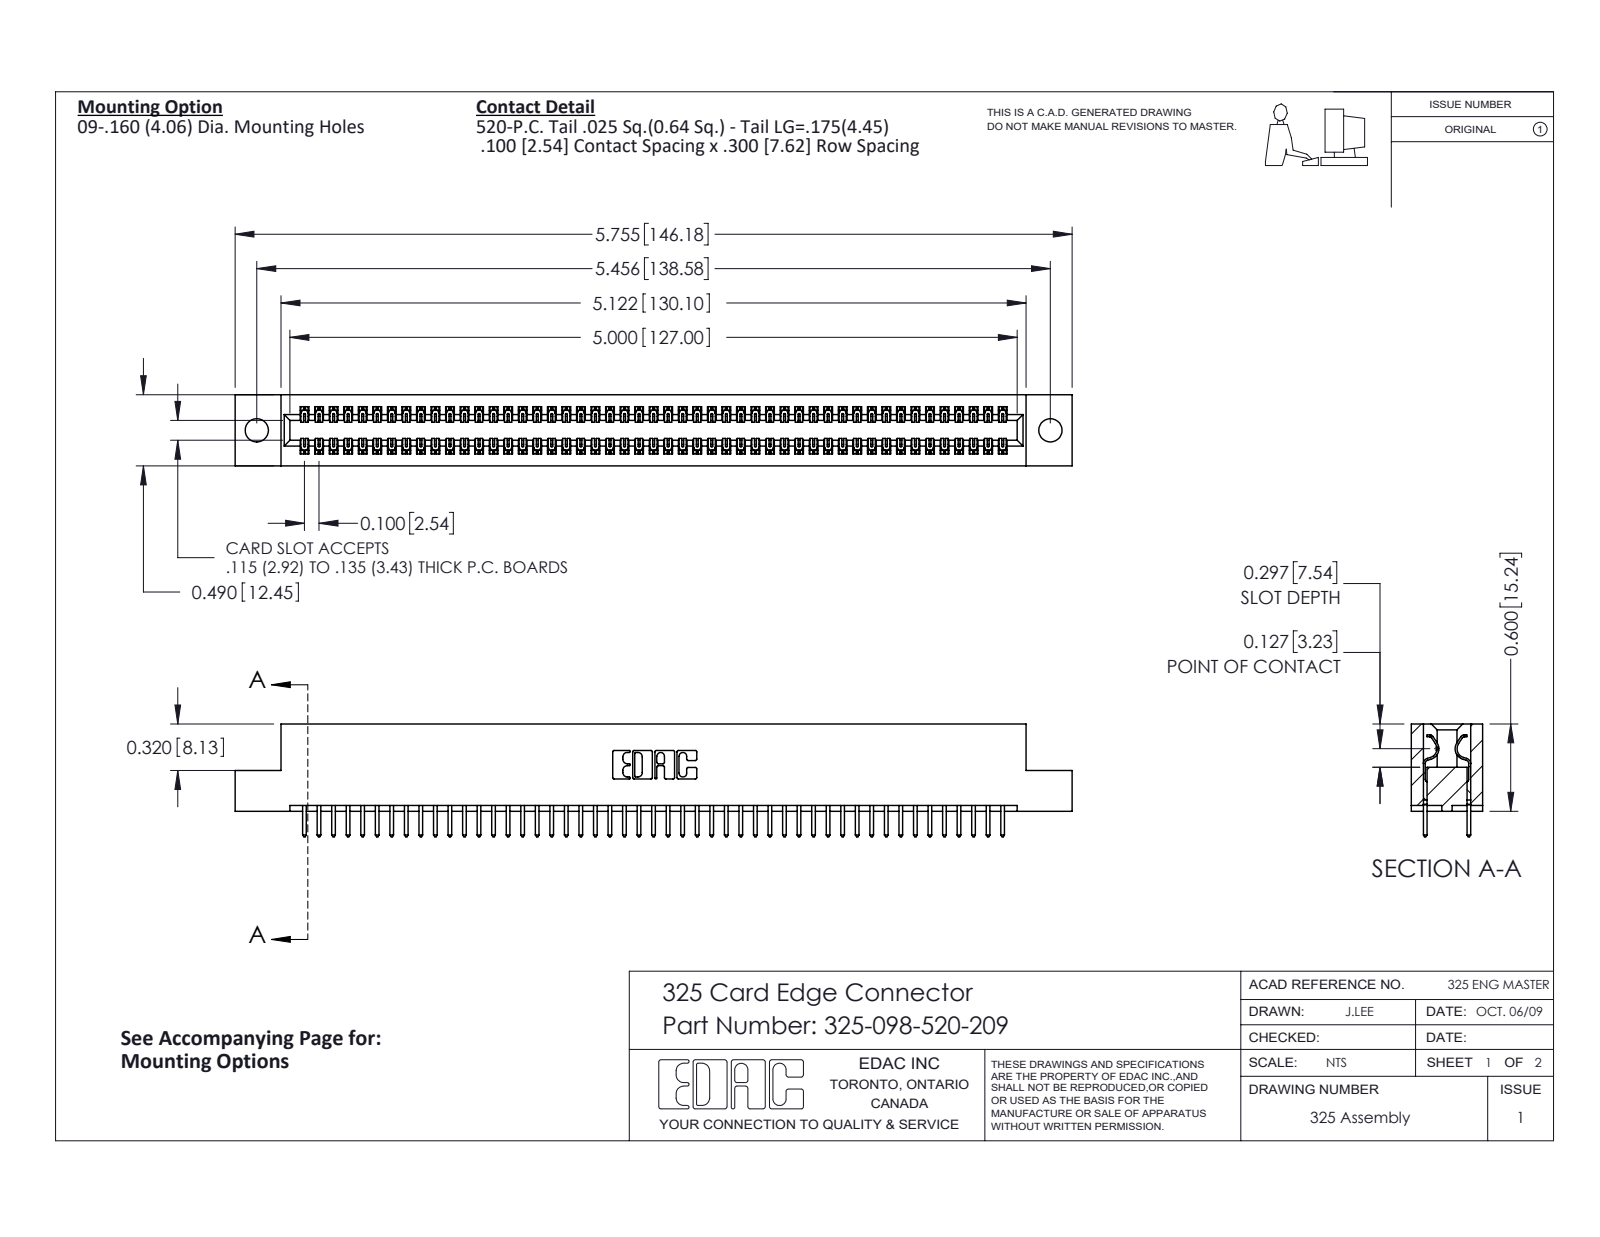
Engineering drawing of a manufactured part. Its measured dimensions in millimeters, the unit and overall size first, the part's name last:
Units: millimetres
Overall size (bounding box): 146.2 × 19.7 × 12.4
Round holes (diameter × count): ⌀4.1 ×2
Partial cylindrical surfaces — rounded edges, fillets, slot ends (radius × count): R0.2 ×147, R0.3 ×98, R0.3 ×22, R0.2 ×6, R0.8 ×6, R0.7 ×3, R0.4 ×2, R0.6 ×2
Main face-to-face distances: 2.1, 10.3, 7.6, 12.4, 2.7, 9.7, 0.6, 8.3, 7, 14.2
Hole centre spacings: 138.6
Volume: 18 680 mm³ · Surface area: 22 510 mm²
Bodies: 99 solids, 5210 faces (3598 planar, 1612 cylindrical, 0 other)
Part name (STEP PRODUCT): 325 Part_.160 TH; 325-292-001_325-293-120; 325-098-520-209
STEP written by: SolidWorks 2016 (CONFIG_CONTROL_DESIGN)
